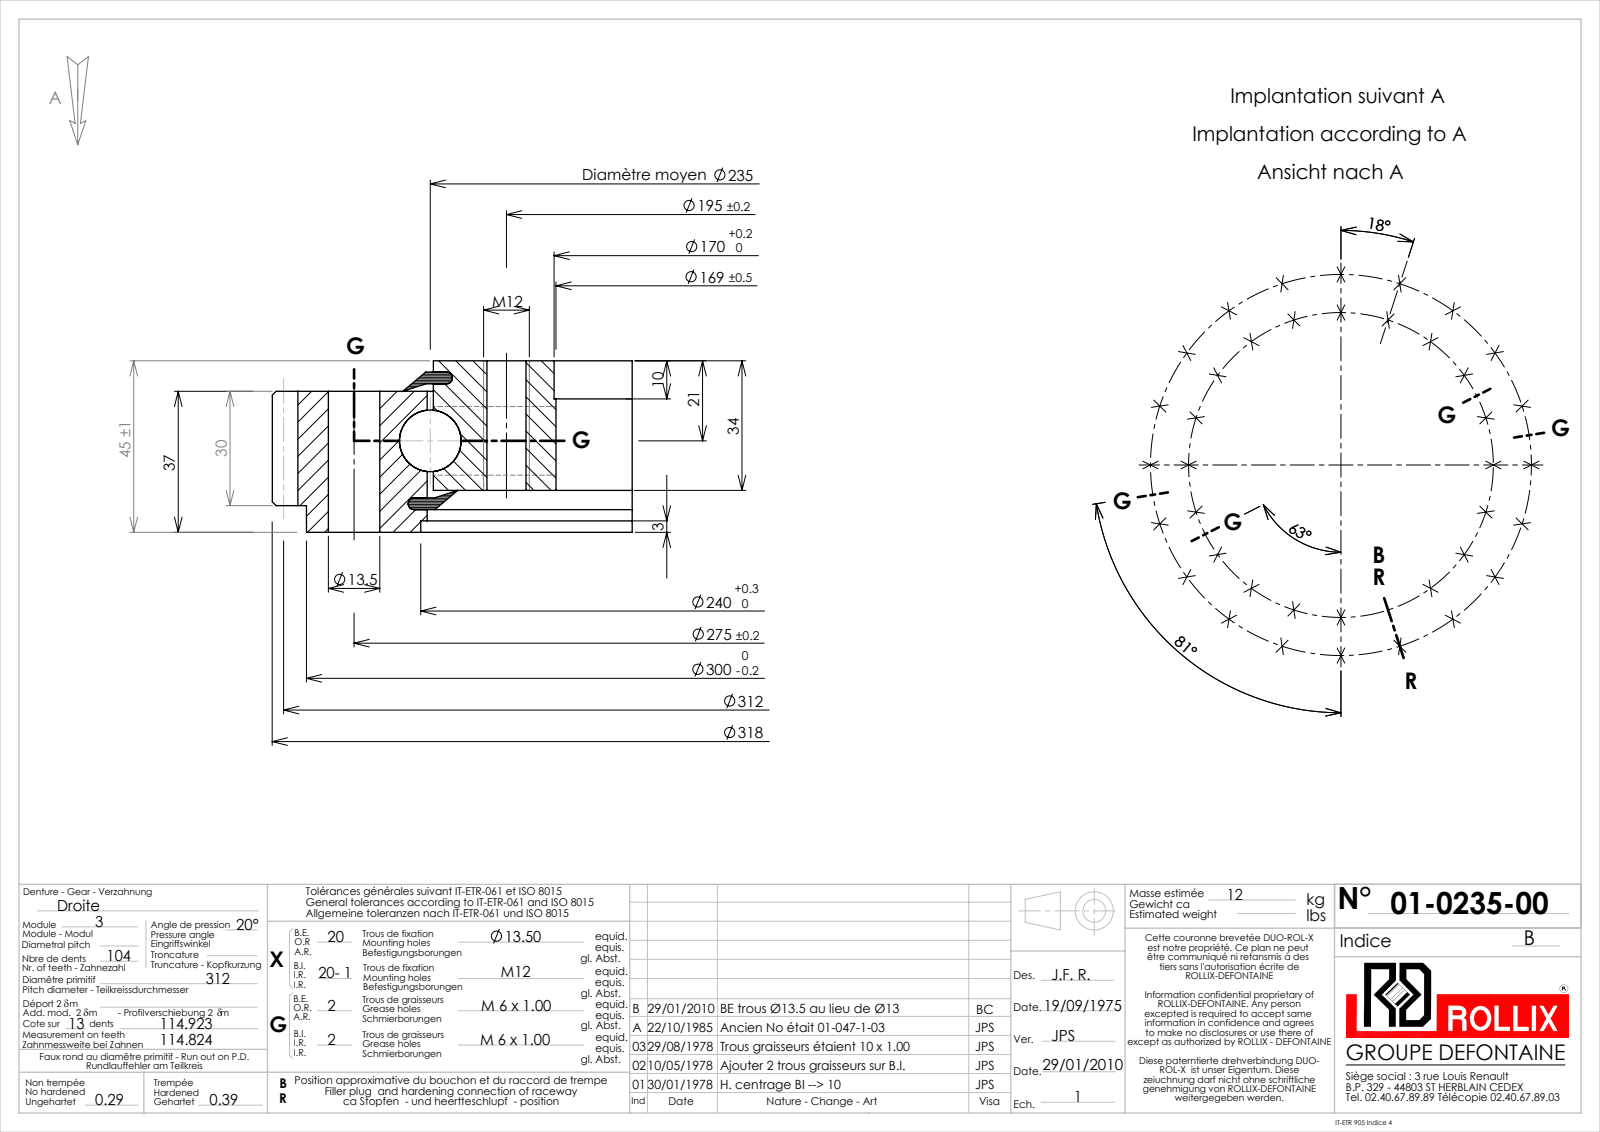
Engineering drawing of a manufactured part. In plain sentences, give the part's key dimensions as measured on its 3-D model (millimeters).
The part is named "01-0235-00". Its 3-D file was written by "SolidWorks 2016 (CONFIG_CONTROL_DESIGN)". It is 5 solids with 778 faces: 223 planar, 315 cylindrical and 240 other. Overall it measures 317.93 by 317.93 by 45 millimeters. Its volume is 1 574 000 cubic millimeters and its surface area 354 861 square millimeters. Round holes: 20 of diameter 13.5, 19 of diameter 10.25, 4 of diameter 5, 1 of diameter 169, 1 of diameter 170, 1 of diameter 236.62, 1 of diameter 240. Round bosses or shafts: 1 of diameter 300, 1 of diameter 233.38. Partial cylindrical surfaces (rounded edges, fillets, slot ends): 1 of radius 152.25, 1 of radius 159. The main face-to-face distances are 37, 8, 34, 11, 26, 45, 1.95, 27.95, 3.1, 5.05. The hole center spacings are 137.5, 43.02, 84.98, 124.85, 161.64, 194.45, 222.48, 245.03.
